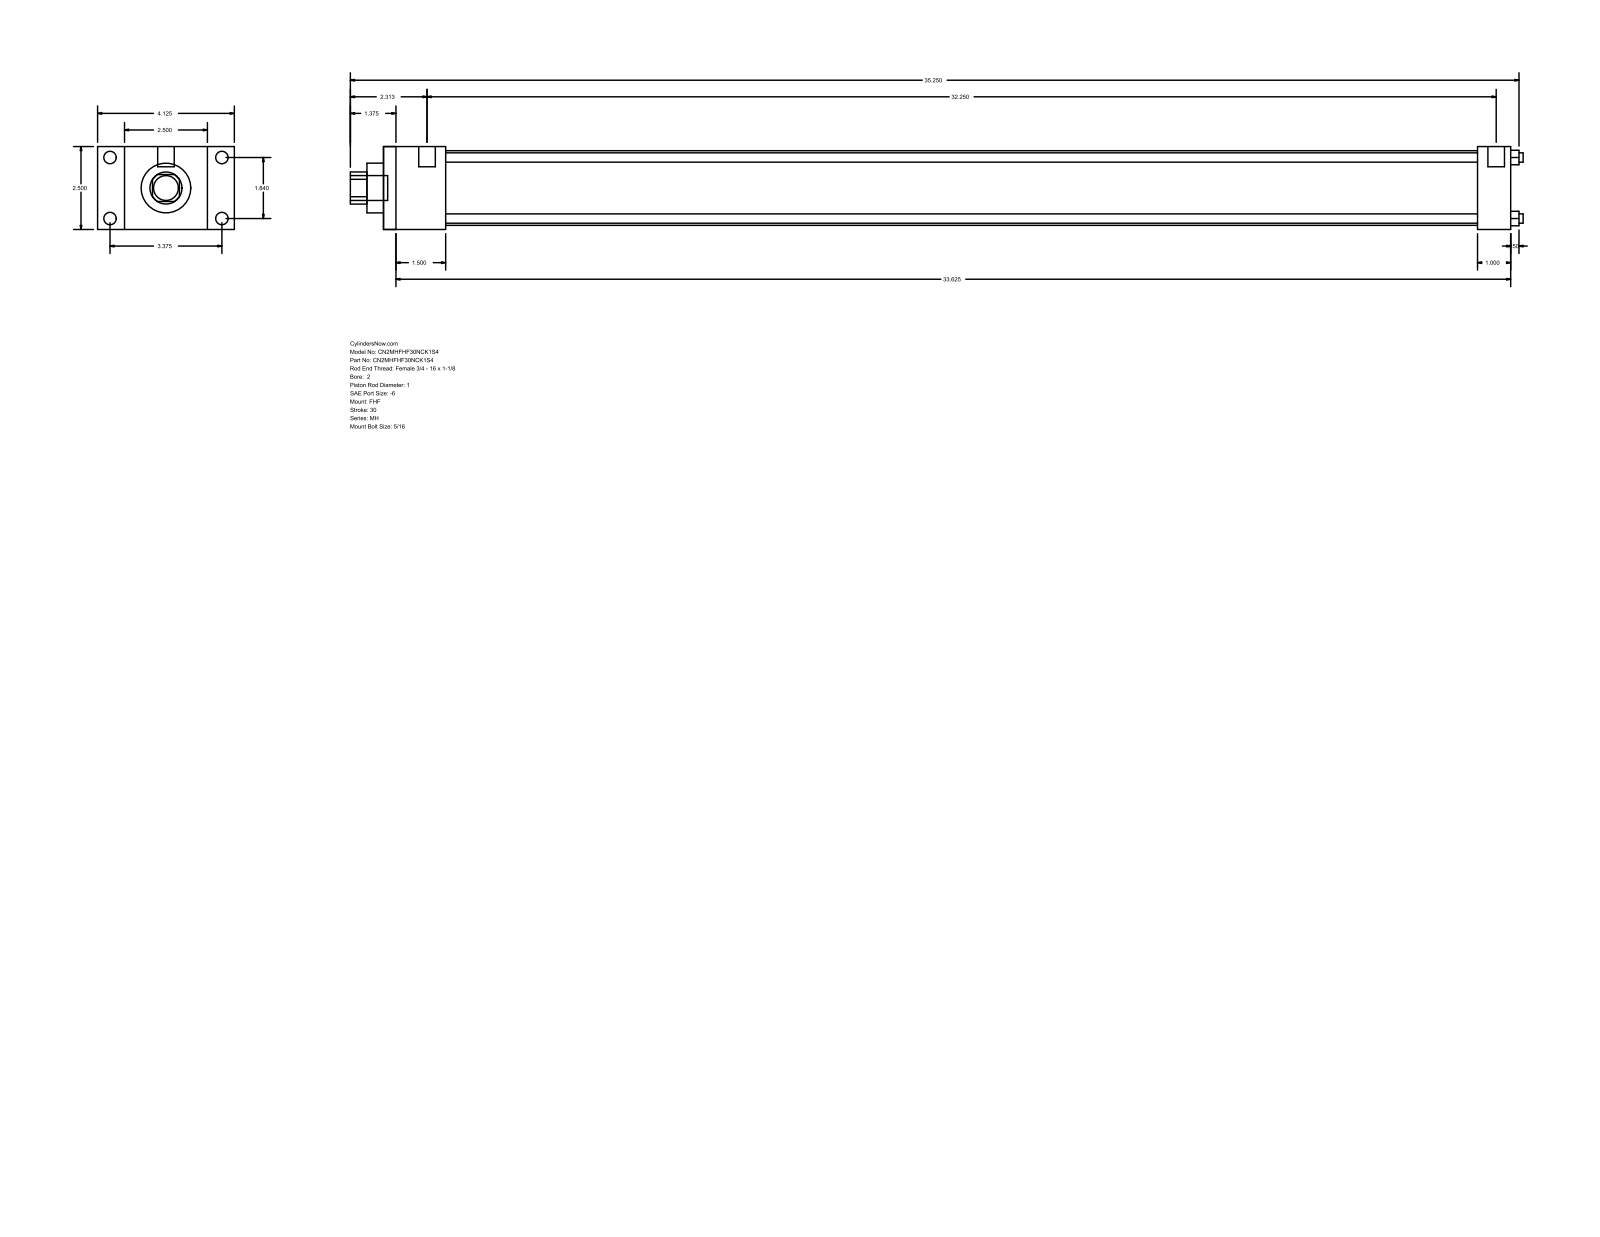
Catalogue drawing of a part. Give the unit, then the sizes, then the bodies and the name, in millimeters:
Units: millimetres
Overall size (bounding box): 898.52 × 104.78 × 63.5
Round holes (diameter × count): ⌀7.14 ×4, ⌀25.4 ×1, ⌀38.1 ×1, ⌀57.15 ×1
Round bosses / shafts (diameter × count): ⌀9.53 ×4, ⌀5.56 ×4, ⌀12.7 ×2, ⌀19.05 ×1
Partial cylindrical surfaces — rounded edges, fillets, slot ends (radius × count): R12.29 ×1
Main face-to-face distances: 63.5, 863.6, 47.63, 815.97, 20.64, 84.14, 104.78, 25.4, 838.2, 790.57
Hole centre spacings: 33.05, 46.74, 66.1
Bodies: 0 solids, 88 faces (60 planar, 28 cylindrical, 0 other)
Part name (STEP PRODUCT): MH_FHF__0200_1
STEP written by: GSSL Pune (CONFIG_CONTROL_DESIGN)
